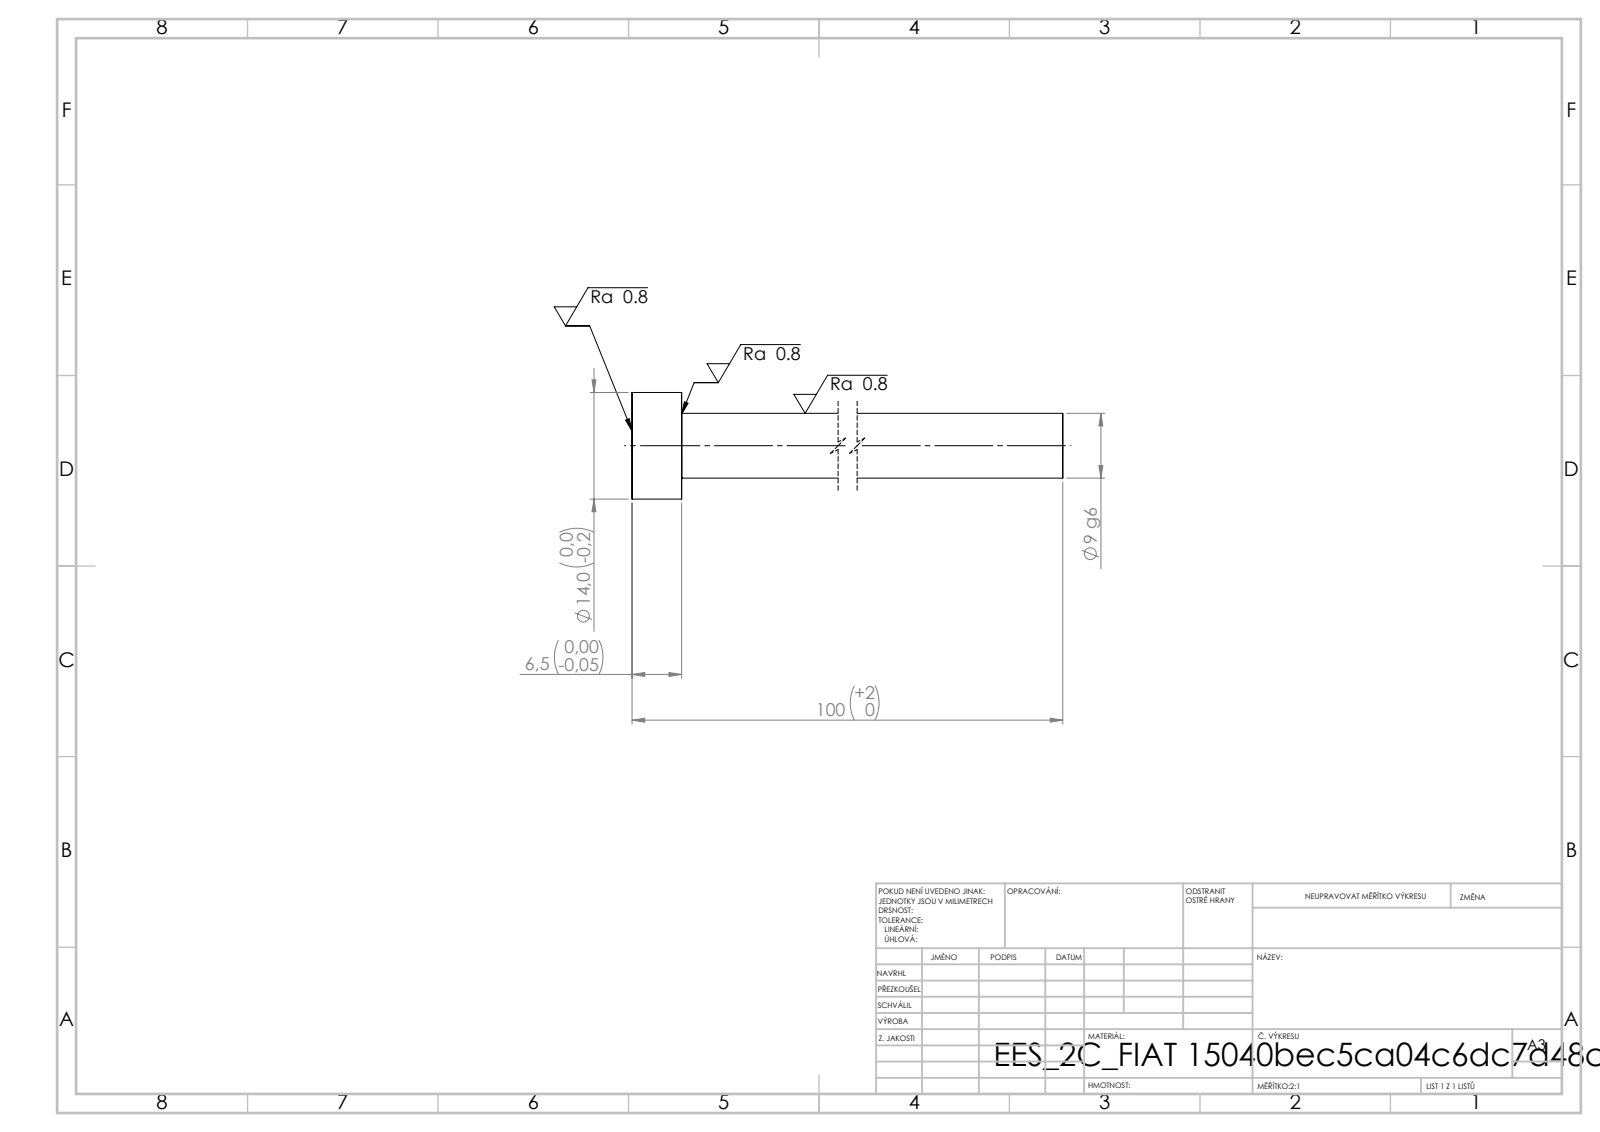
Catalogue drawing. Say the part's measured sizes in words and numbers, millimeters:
Its 3-D file was written by "SolidWorks 2019 (CONFIG_CONTROL_DESIGN)". It is 1 solid with 7 faces: 3 planar, 4 cylindrical and 0 other. Overall it measures 100 by 14 by 14 millimeters. Its volume is 6 306 cubic millimeters and its surface area 3 091 square millimeters. Round bosses or shafts: 1 of diameter 14, 1 of diameter 8.5. The main face-to-face distances are 6.5, 100, 93.5.
